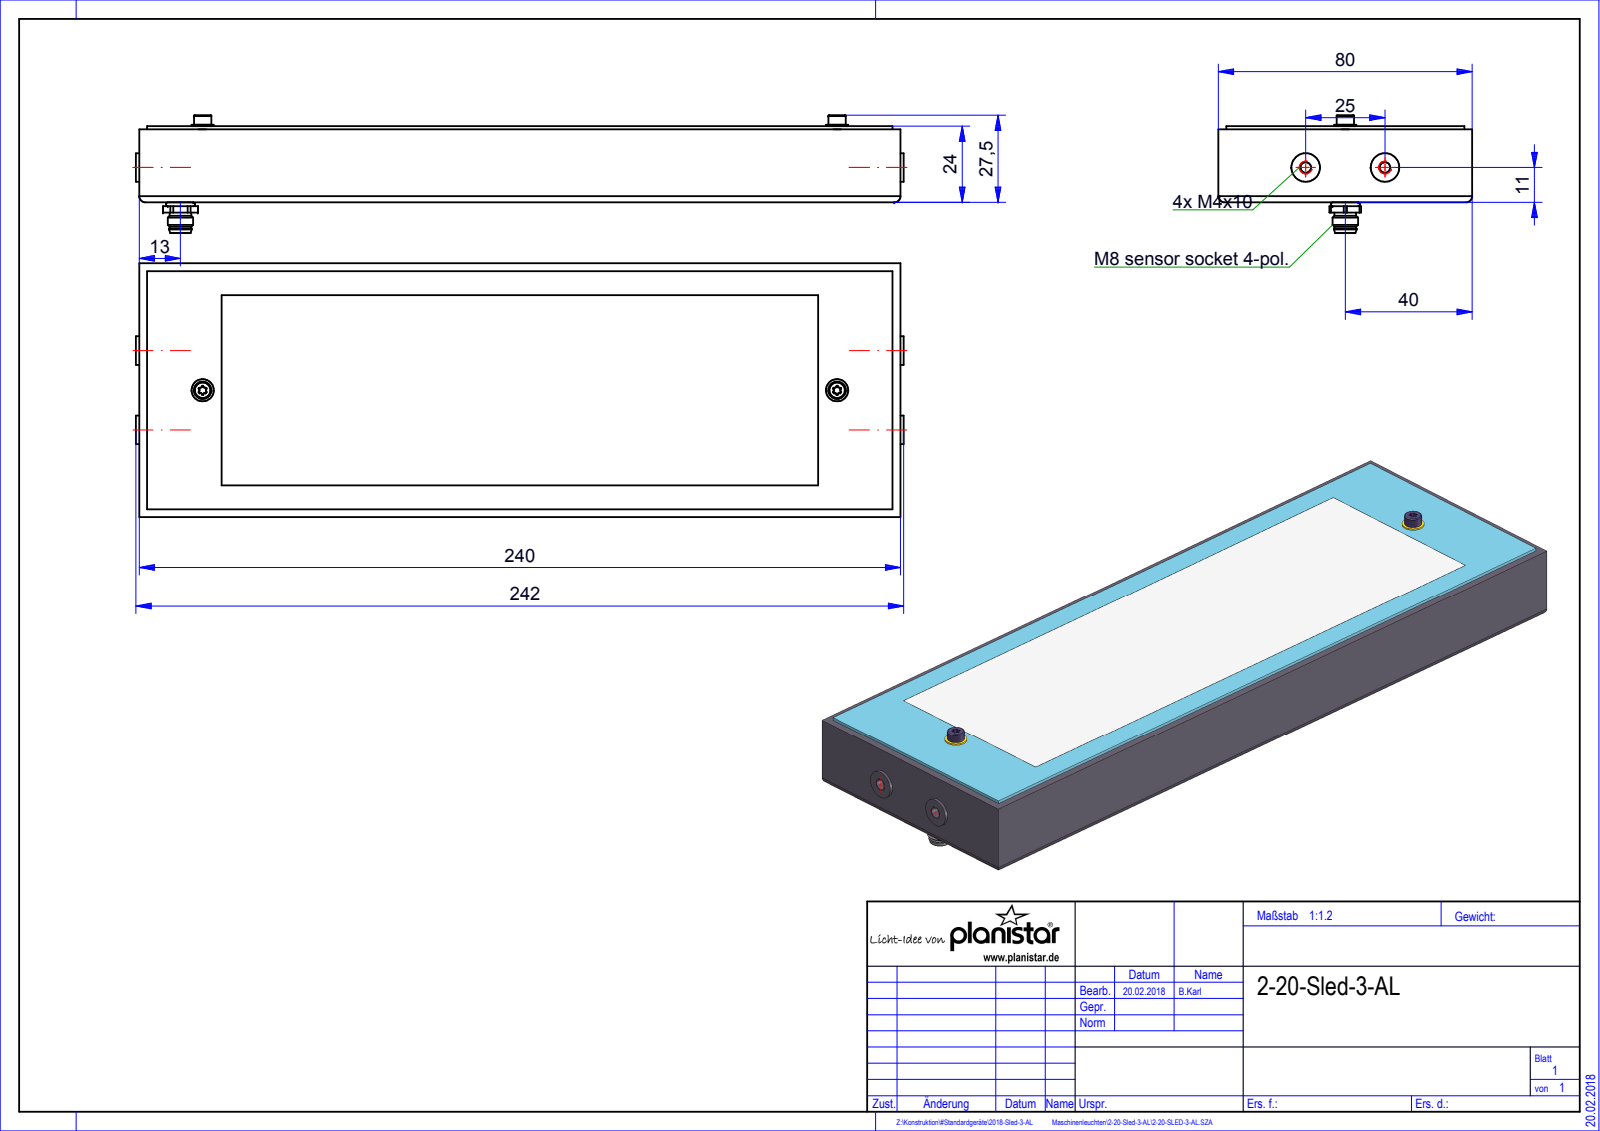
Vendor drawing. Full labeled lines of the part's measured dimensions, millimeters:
Part name (STEP PRODUCT): Root; Baugruppe_Xled-2-VD; QUADER_0; 09-3391-00-04 (+2 more)
STEP written by: HiCAD 2015 2002.1 Build 408 (AUTOMOTIVE_DESIGN)
Units: millimetres
Bodies: 6 solids, 132 faces (48 planar, 67 cylindrical, 17 other)
Overall size (bounding box): 242 × 80 × 37.2
Volume: 458 352 mm³ · Surface area: 55 198 mm²
Round holes (diameter × count): ⌀3.2 ×2, ⌀3.3 ×2, ⌀4 ×2, ⌀5.8 ×1
Round bosses / shafts (diameter × count): ⌀1 ×4, ⌀9 ×2, ⌀7 ×2, ⌀5.5 ×2, ⌀3 ×2, ⌀2.46 ×2, ⌀8 ×1, ⌀7.2 ×1
Partial cylindrical surfaces — rounded edges, fillets, slot ends (radius × count): R0.23 ×12, R0.58 ×12, R2 ×4, R5.5 ×1
Main face-to-face distances: 23.95, 24, 80, 1, 23, 0.95, 240, 2.5, 77.5, 75
Hole centre spacings: 7, 25, 200, 207
